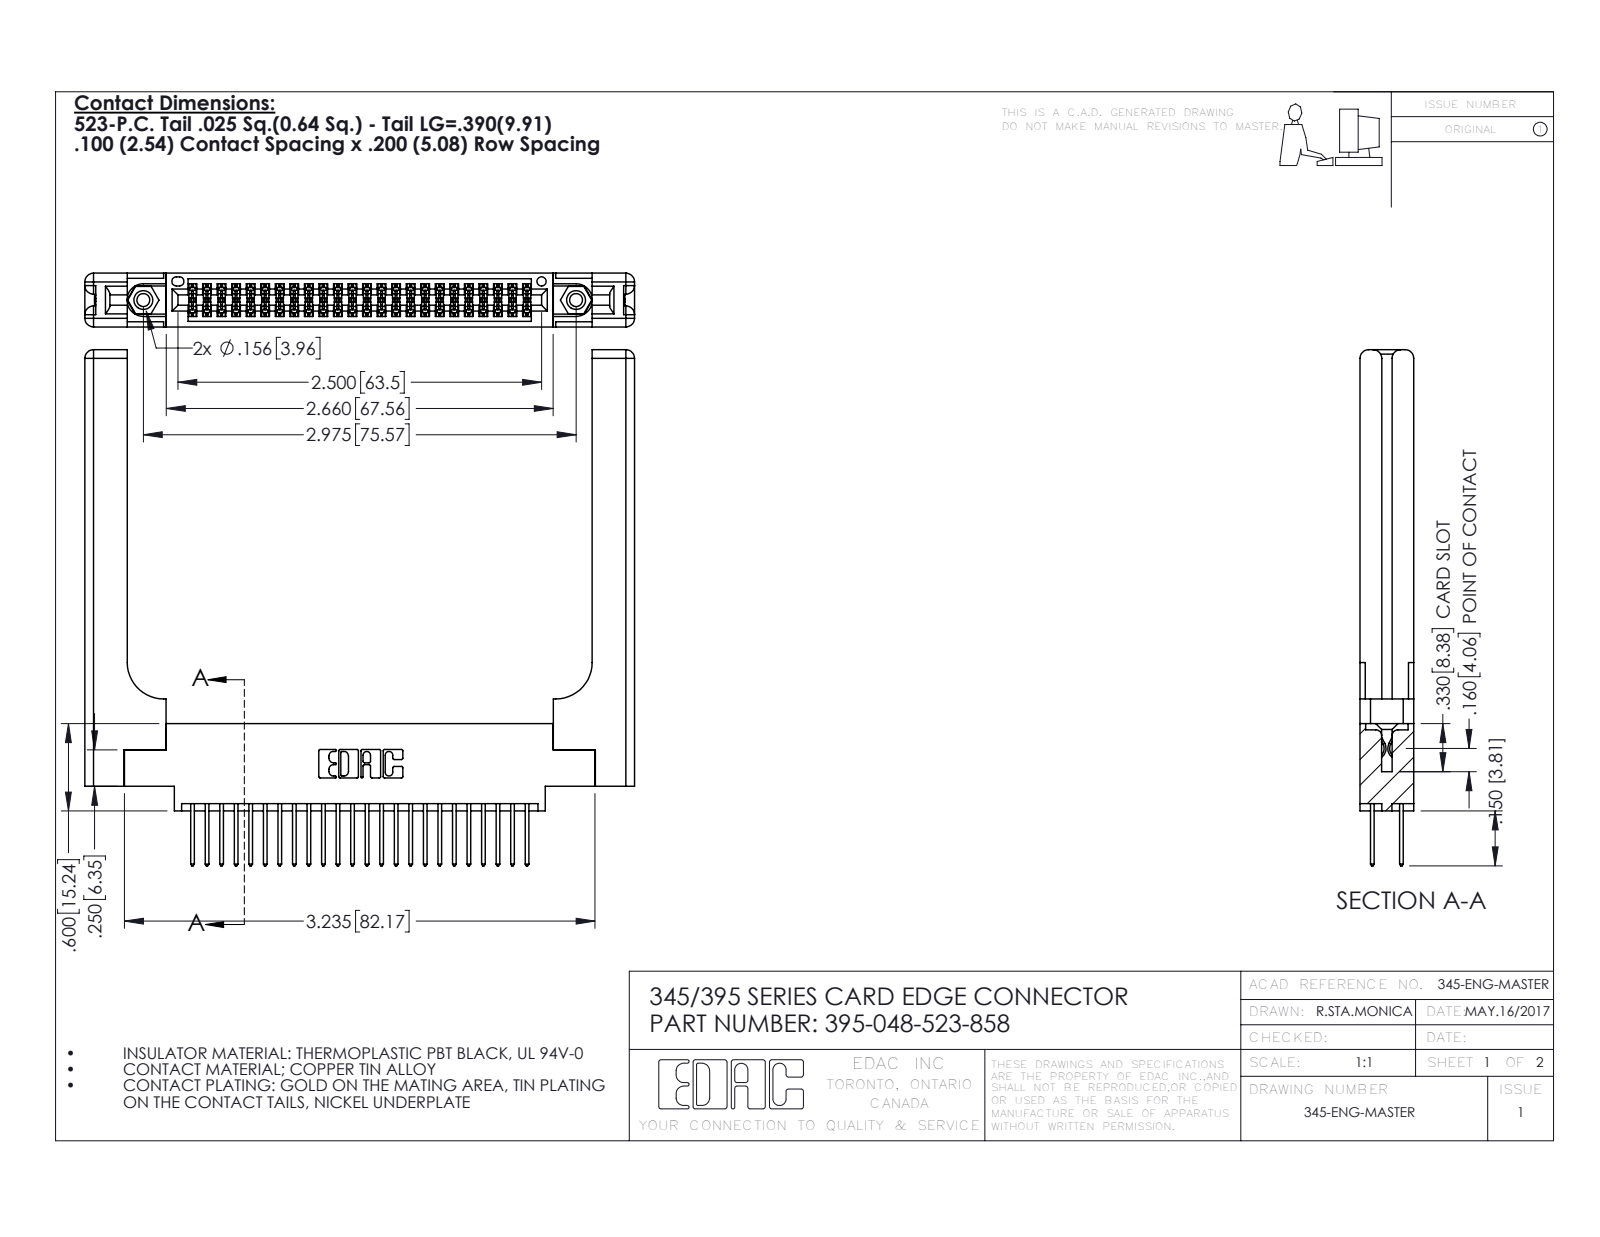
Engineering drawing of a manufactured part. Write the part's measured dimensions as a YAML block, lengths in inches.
part_name: "395-048-523-858; 345-220-058_345-220-058; 345-250-001_345-250-001-102; 345 Part_0.170 Offset - 0.156 Dia-TH (+1 more)"
step_written_by: "SolidWorks 2016 (CONFIG_CONTROL_DESIGN)"
units: inches
bodies: {solids: 53, faces: 2786, planar: 1816, cylindrical: 910, other: 60}
overall_size: [3.779, 3.547, 0.37]
volume: 1.075
surface_area: 29.15
round_holes:
  - {diameter: 0.089, count: 2}
  - {diameter: 0.125, count: 2}
  - {diameter: 0.156, count: 2}
  - {diameter: 0.064, count: 1}
round_bosses_or_shafts:
  - {diameter: 0.155, count: 2}
partial_cylinders:
  - {radius: 0.006, count: 72}
  - {radius: 0.01, count: 48}
  - {radius: 0.01, count: 22}
  - {radius: 0.06, count: 16}
  - {radius: 0.007, count: 6}
  - {radius: 0.031, count: 6}
  - {radius: 0.026, count: 3}
  - {radius: 0.014, count: 2}
face_to_face_distances: [0.37, 0.072, 0.298, 0.098, 0.272, 0.025, 0.2, 0.225, 0.148, 0.15]
hole_center_spacings: [0.27, 2.741, 2.975]
